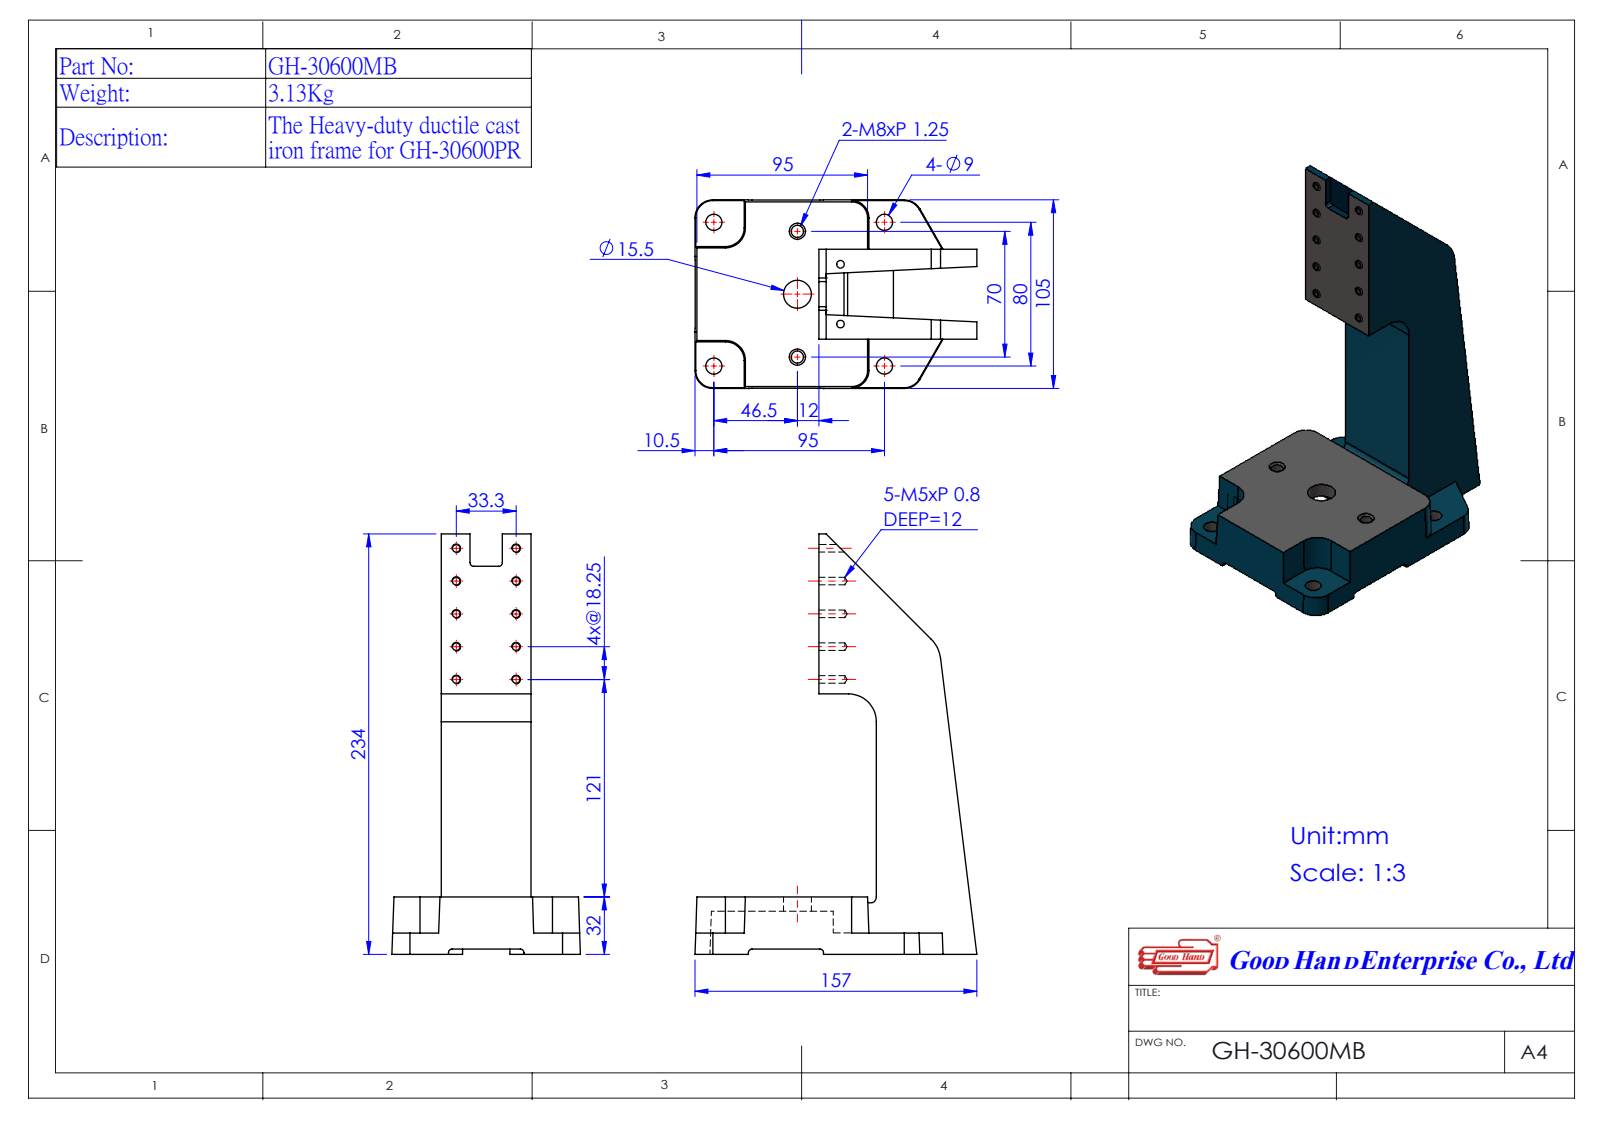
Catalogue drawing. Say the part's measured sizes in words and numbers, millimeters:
The part is named "GH-30600MB(簡化)-1^GH-30600PR(簡化)-2". Its 3-D file was written by "SolidWorks 2016 (AUTOMOTIVE_DESIGN)". It is 1 solid with 137 faces: 61 planar, 46 cylindrical and 30 other. Overall it measures 234 by 157 by 105 millimeters. Its volume is 464 524 cubic millimeters and its surface area 108 313 square millimeters. Round holes: 10 of diameter 4.2, 4 of diameter 9, 2 of diameter 6.8, 1 of diameter 15.5. Partial cylindrical surfaces (rounded edges, fillets, slot ends): 4 of radius 2, 1 of radius 3.33, 1 of radius 10, 1 of radius 15.5, 1 of radius 18, 1 of radius 25.5. The main face-to-face distances are 50, 32, 24, 8, 11.93, 12.07, 20.07, 9.5, 41.5, 7.15. The hole center spacings are 18.25, 37.97, 36.5, 49.41, 33.3, 54.75, 64.08, 35.
